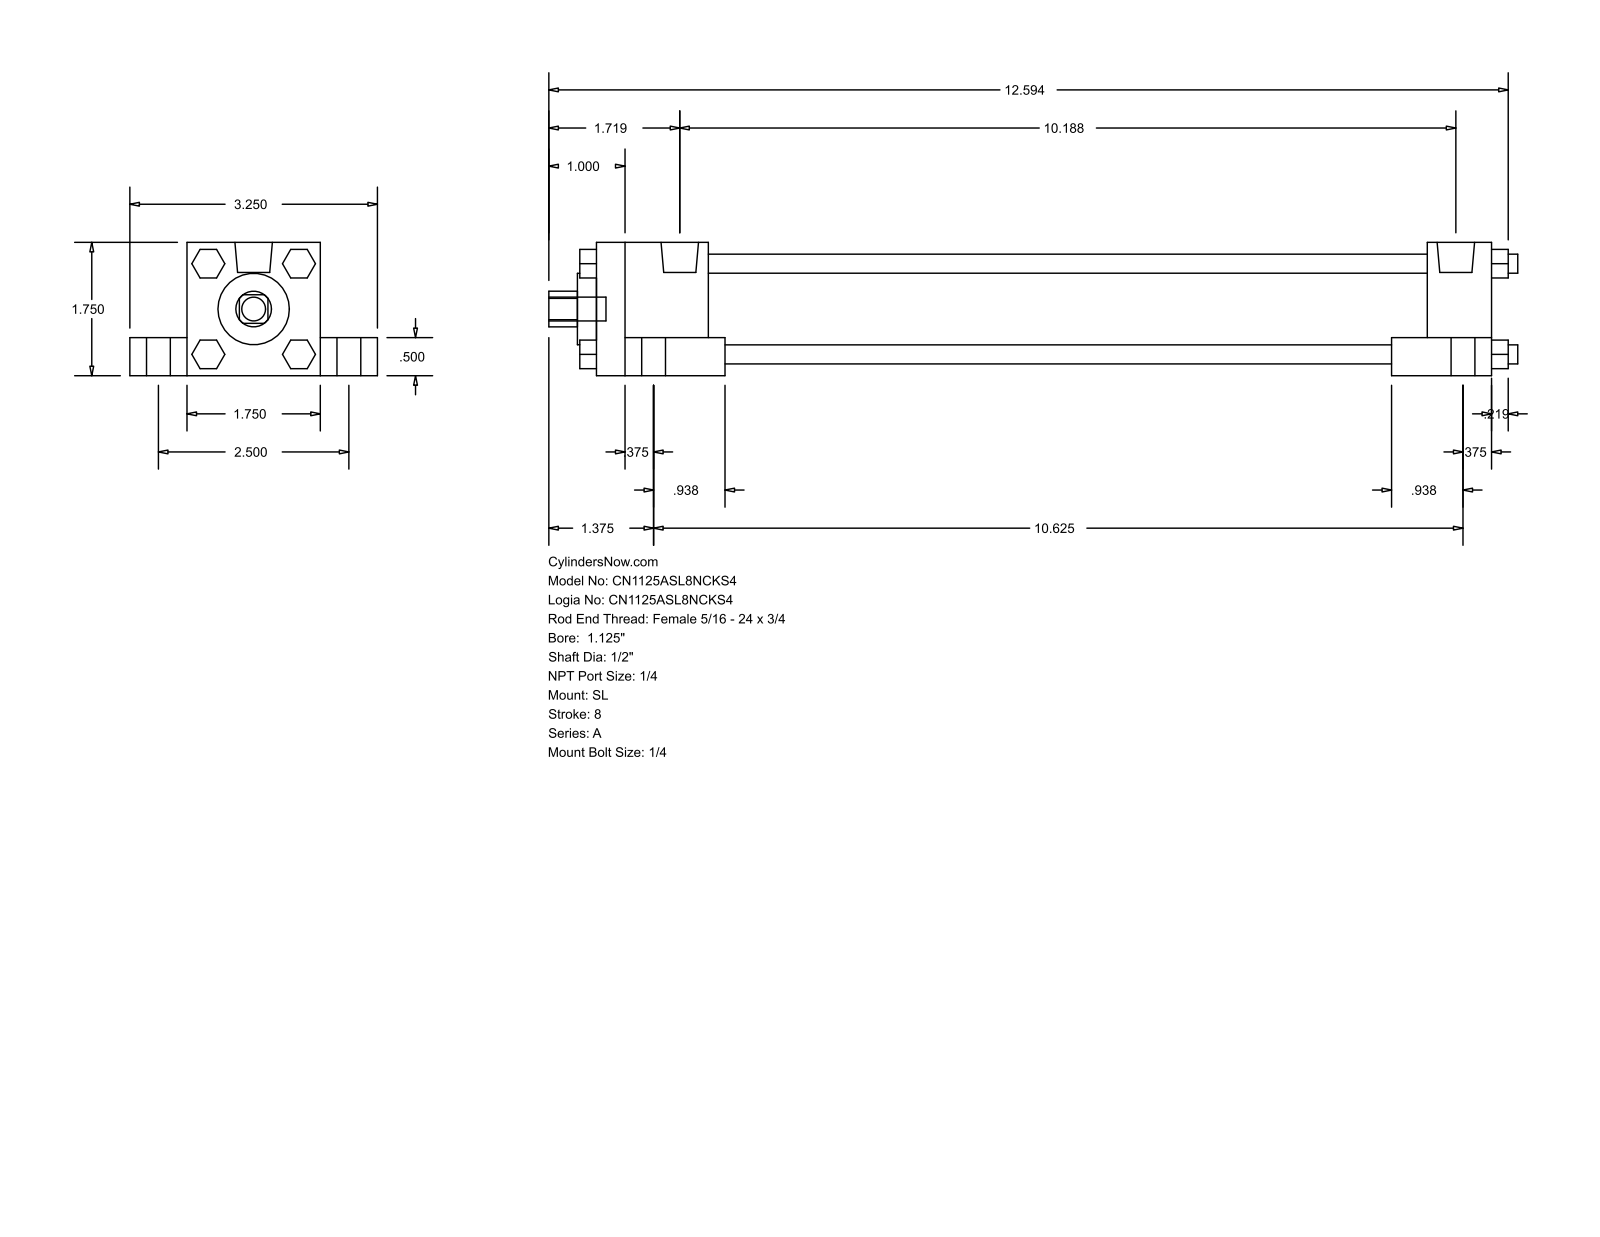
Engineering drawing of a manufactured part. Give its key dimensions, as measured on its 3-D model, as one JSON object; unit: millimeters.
{"part_name": "A_SL__0112_0.5", "step_written_by": "GSSL Pune (CONFIG_CONTROL_DESIGN)", "units": "millimeters", "bodies": {"solids": 0, "faces": 150, "planar": 114, "cylindrical": 36, "other": 0}, "overall_size": [323.06, 82.55, 44.45], "round_holes": [[12.7, 1], [23.81, 1], [31.88, 1]], "round_bosses_or_shafts": [[7.94, 5], [14.29, 4], [6.35, 4], [5.56, 4], [12.49, 2]], "partial_cylinders_radius": [[5.94, 1]], "face_to_face_distances": [44.46, 31.76, 12.7, 19.04, 63.5, 261.14, 298.44, 277.01, 21.43, 37.3]}
